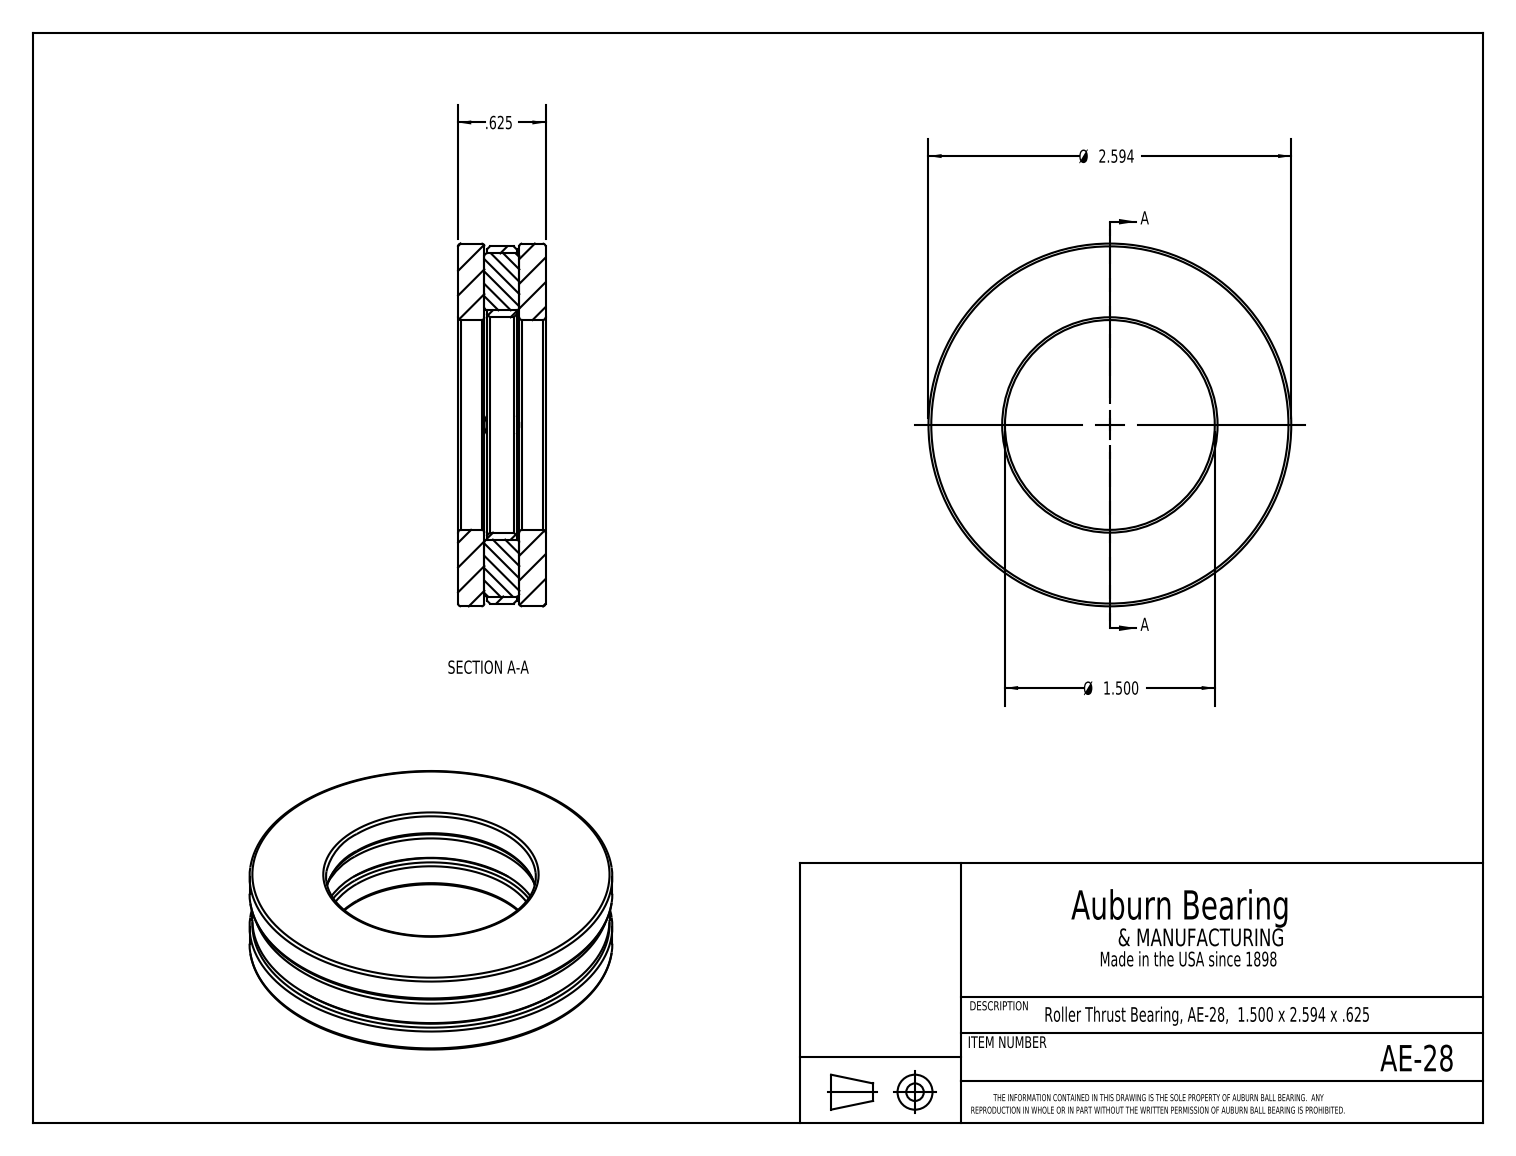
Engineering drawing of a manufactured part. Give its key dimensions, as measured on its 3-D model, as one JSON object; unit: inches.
{"part_name": "AE-28", "step_written_by": "SolidWorks 2017 (CONFIG_CONTROL_DESIGN)", "units": "inches", "bodies": {"solids": 7, "faces": 60, "planar": 30, "cylindrical": 10, "other": 20}, "overall_size": [2.594, 2.594, 0.625], "volume_in3": 1.988, "surface_area_in2": 29.27, "round_holes": [[1.5, 1], [1.54, 1]], "round_bosses_or_shafts": [[0.25, 2], [2.594, 1], [2.554, 1]], "face_to_face_distances": [0.207, 0.418, 0.25, 0.187, 0.437, 0.625, 0.438, 0.188, 0.23, 0.02]}
